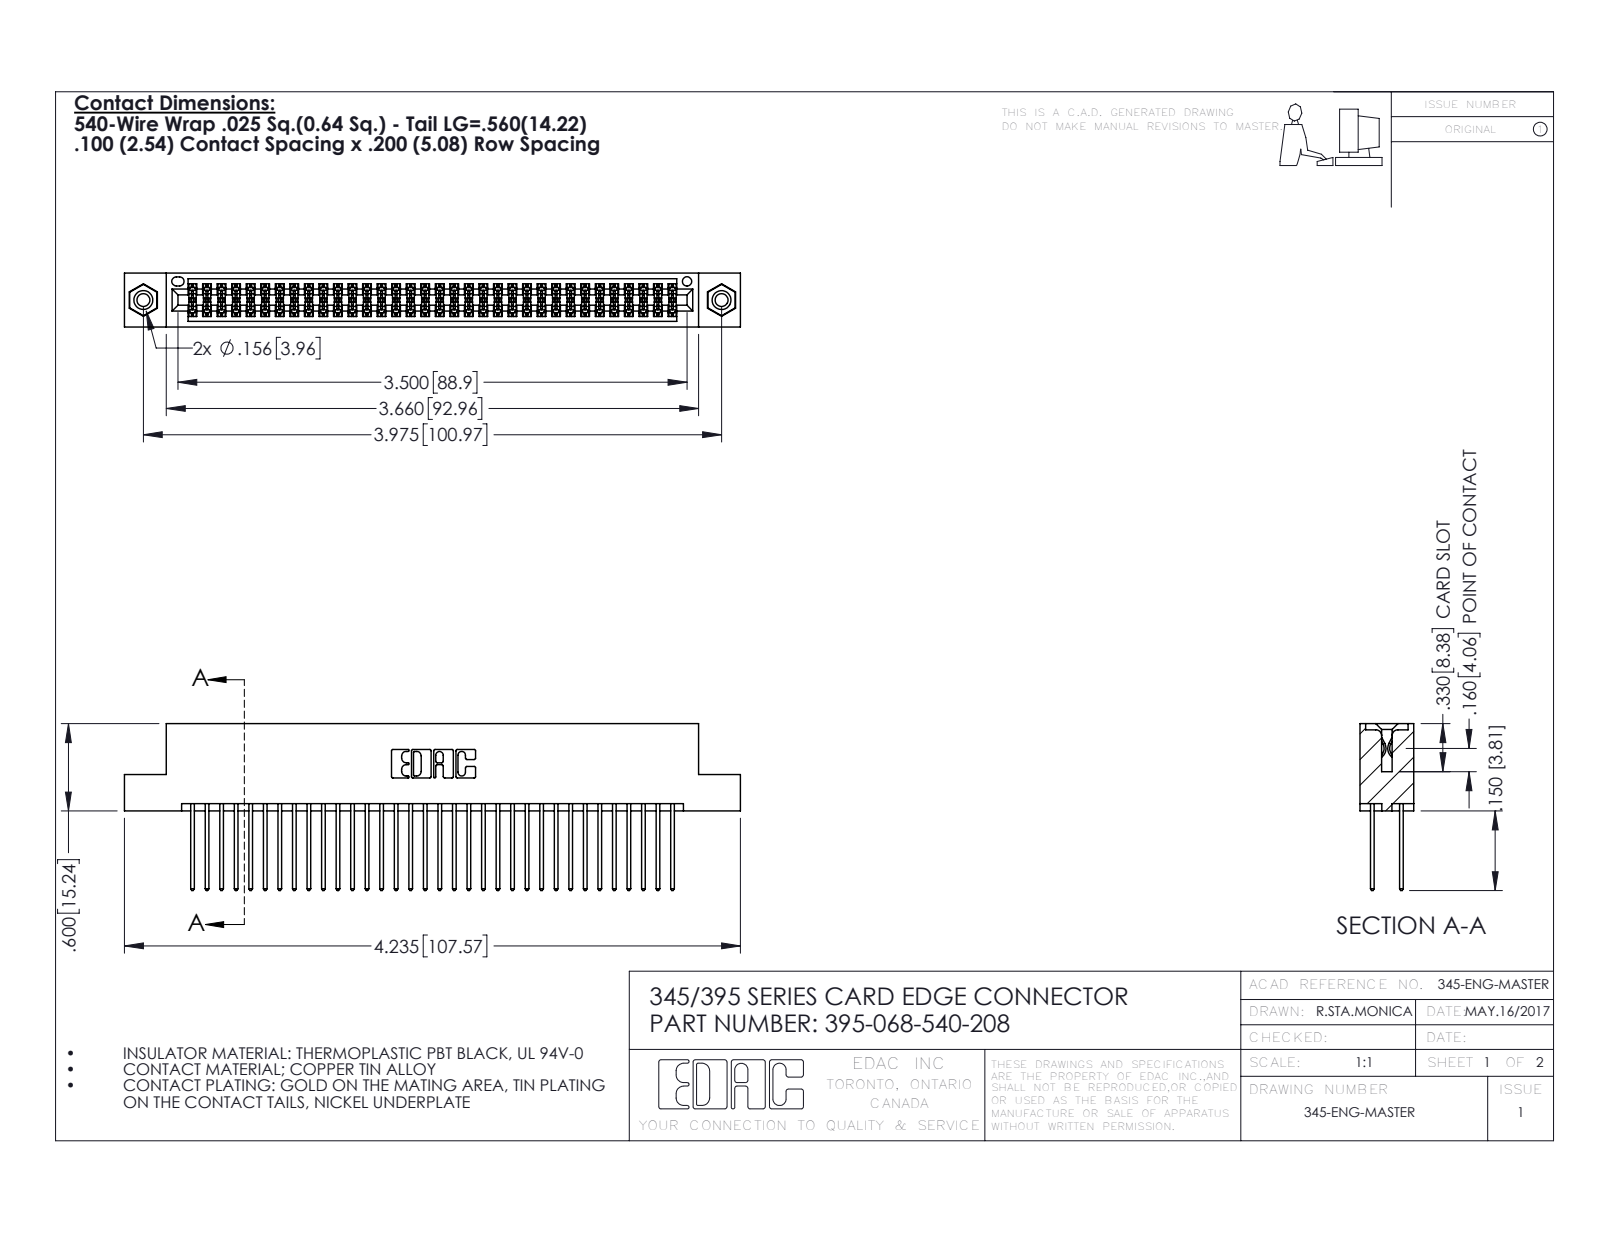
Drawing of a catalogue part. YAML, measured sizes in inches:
part_name: "345-292-001_345-293-140; 395-068-540-208; 345 Part_Flush Mounting Lugs - 0.156 Dia-TI; 345-250-001_345-250-003-102"
step_written_by: "SolidWorks 2016 (CONFIG_CONTROL_DESIGN)"
units: inches
bodies: {solids: 71, faces: 3586, planar: 2356, cylindrical: 1214, other: 16}
overall_size: [4.235, 1.147, 0.37]
volume: 0.648
surface_area: 25.98
round_holes:
  - {diameter: 0.089, count: 2}
  - {diameter: 0.125, count: 2}
  - {diameter: 0.156, count: 2}
  - {diameter: 0.064, count: 1}
round_bosses_or_shafts:
  - {diameter: 0.155, count: 2}
partial_cylinders:
  - {radius: 0.006, count: 102}
  - {radius: 0.01, count: 68}
  - {radius: 0.01, count: 22}
  - {radius: 0.007, count: 6}
  - {radius: 0.031, count: 6}
  - {radius: 0.026, count: 3}
  - {radius: 0.014, count: 2}
  - {radius: 0.019, count: 2}
face_to_face_distances: [0.072, 0.298, 0.2, 0.098, 0.272, 0.025, 0.37, 0.225, 0.175, 0.149]
hole_center_spacings: [0.27, 3.74, 3.975]
